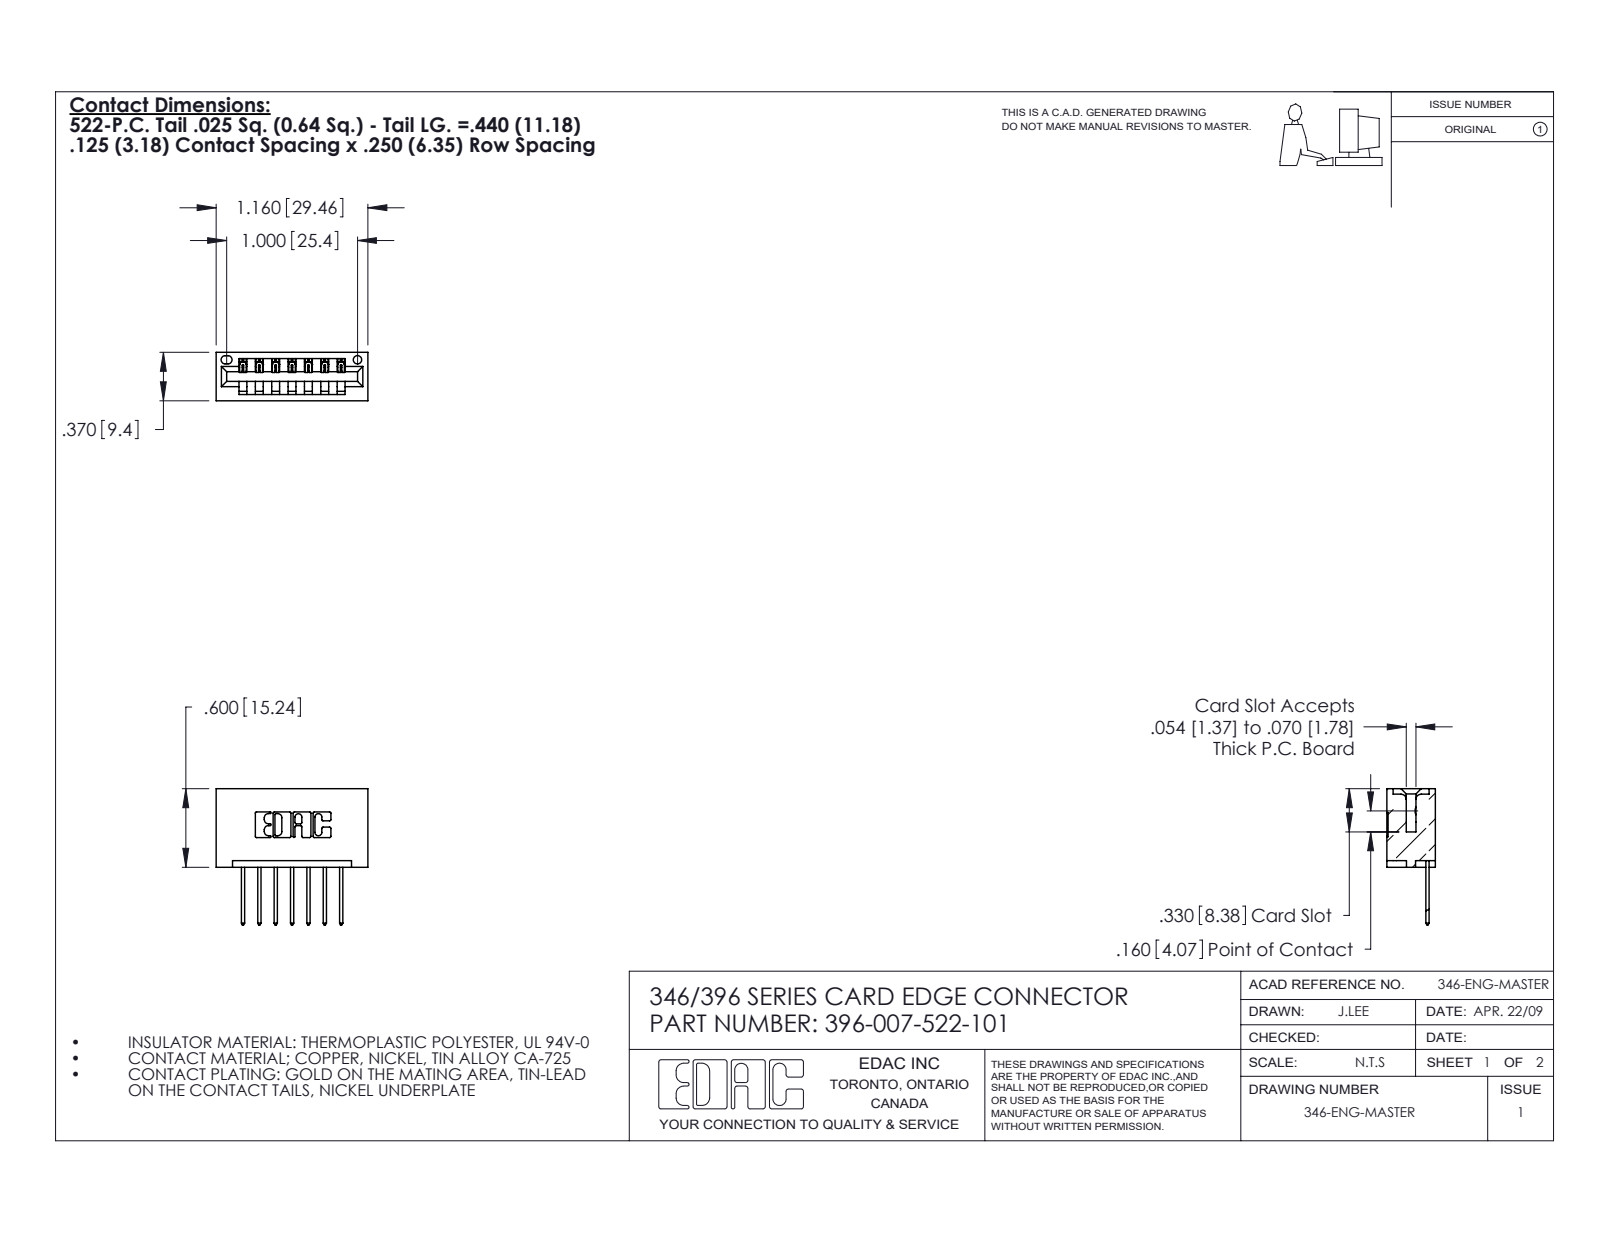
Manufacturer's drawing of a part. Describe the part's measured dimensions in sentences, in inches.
The part is named "345-292-001_345-293-122; 396-007-522-101; 346 Part_No Mounting Lugs". Its 3-D file was written by "SolidWorks 2020 (CONFIG_CONTROL_DESIGN)". It is 8 solids with 520 faces: 352 planar, 168 cylindrical and 0 other. Overall it measures 1.16 by 1.04 by 0.37 inches. Its volume is 0.191 cubic inches and its surface area 5.634 square inches. Round holes: 1 of diameter 0.064. Partial cylindrical surfaces (rounded edges, fillets, slot ends): 22 of radius 0.01, 14 of radius 0.006, 14 of radius 0.01, 6 of radius 0.007, 6 of radius 0.031, 3 of radius 0.026, 2 of radius 0.031, 2 of radius 0.04. The main face-to-face distances are 0.25, 0.048, 0.322, 0.37, 0.072, 0.298, 0.025, 0.125, 0.148, 0.222.
